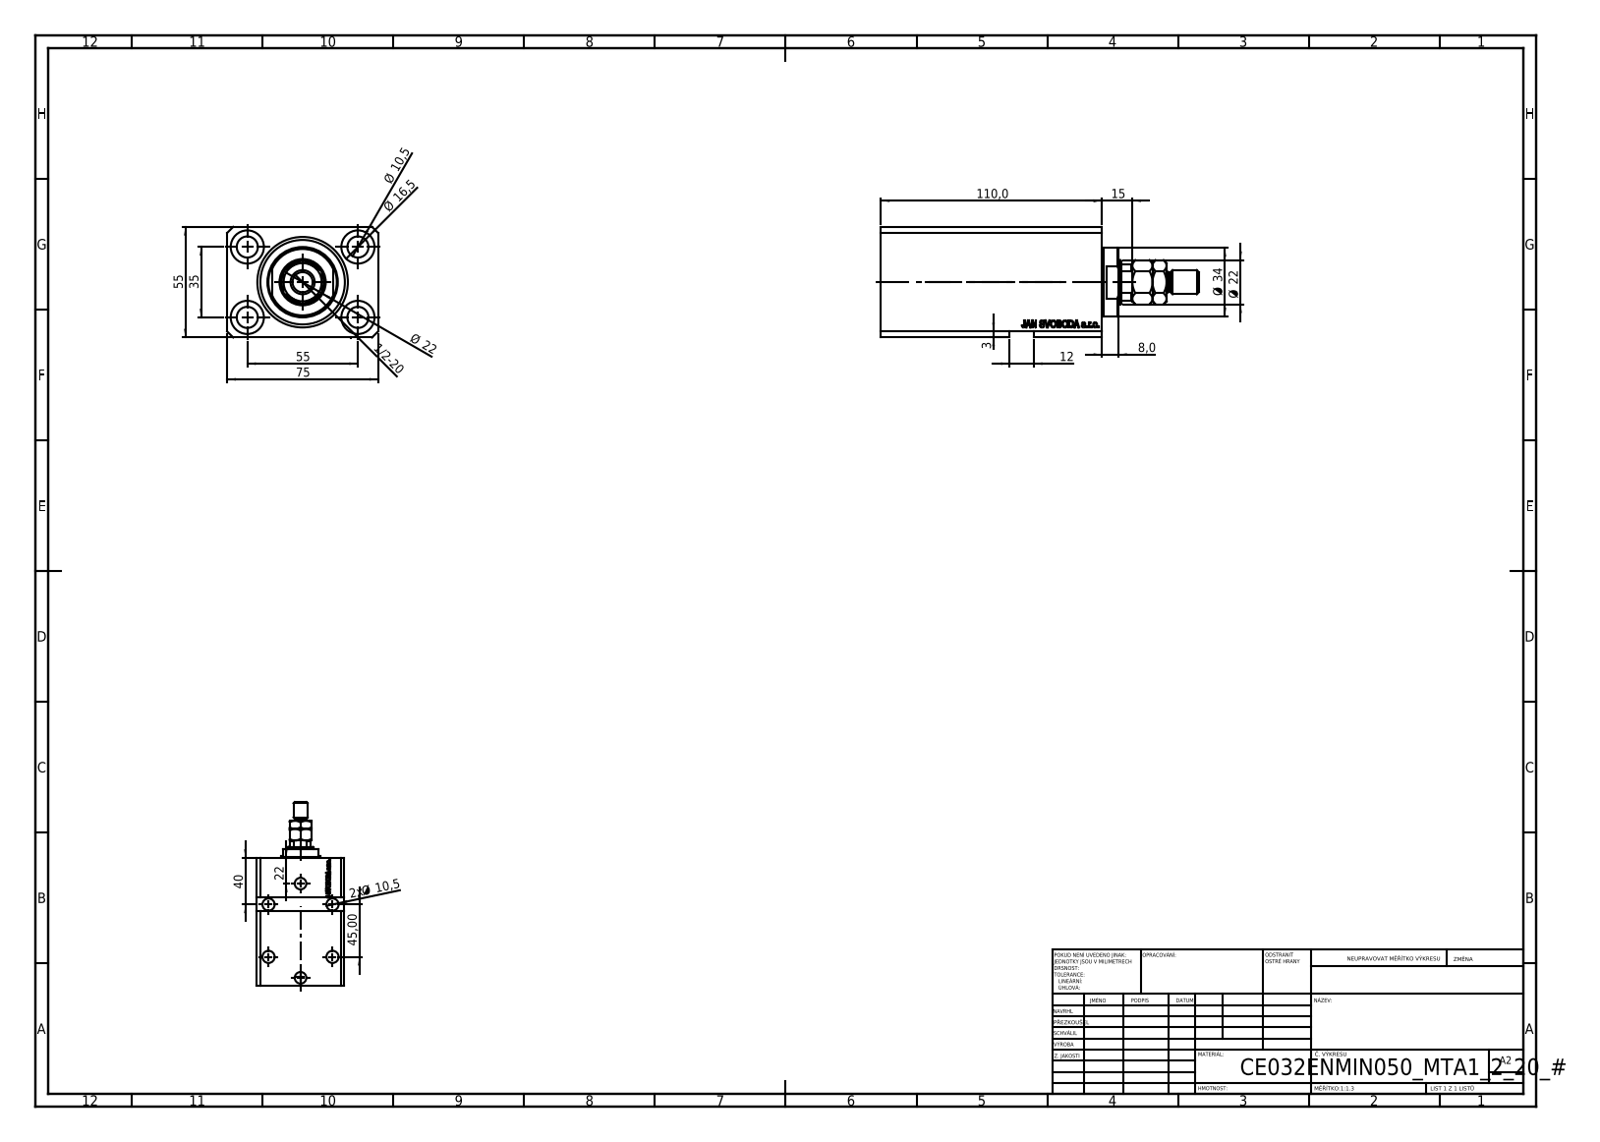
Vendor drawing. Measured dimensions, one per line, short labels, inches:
name: V250CE_VC_E; V250CE_E_Body; V250CE_C_VCP; MTA
written by: SolidWorks 2019 (CONFIG_CONTROL_DESIGN)
unit: in
bodies: 4 solids, 963 faces (453 planar, 108 cylindrical, 402 other)
size: 6.22 × 2.953 × 2.165
volume: 22.95 in³; area: 135.9 in²
holes: 9× ⌀0.413, 4× ⌀0.049, 4× ⌀0.65, 2× ⌀0.394, 2× ⌀0.518, 2× ⌀0.787, 1× ⌀0.866, 1× ⌀1.26, 1× ⌀1.772
bosses: 1× ⌀1.339, 1× ⌀0.472, 1× ⌀0.394
rounds: 1× R0.413
face distances: 2.165, 2.953, 0.591, 4.331, 3.74, 0.39, 3.35, 3.941, 0.748, 0.433
hole spacings: 1.283, 1.294, 2.165, 2.706, 1.283, 1.378, 1.772, 2.567
